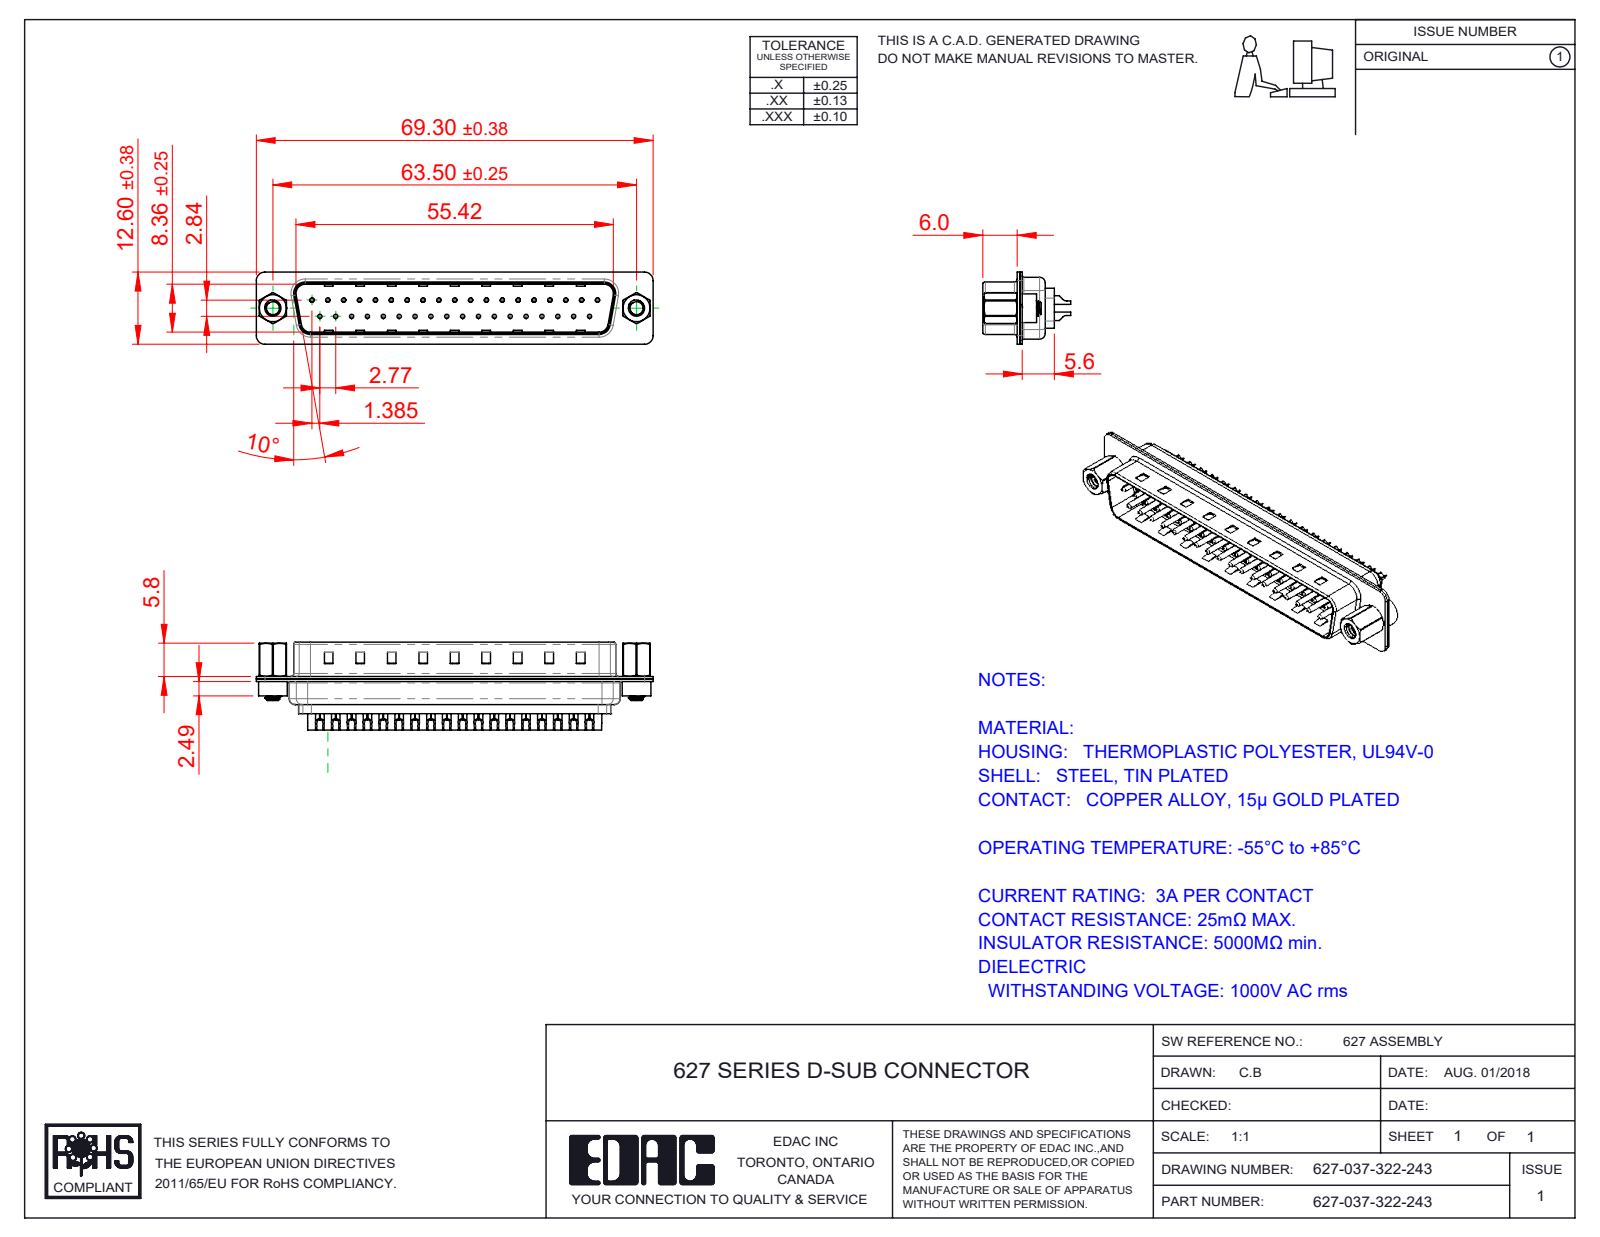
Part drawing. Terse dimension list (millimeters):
name: 627 Contact Row 2_22L; 627 Contact Row 1_22L; 627 4-40 Threaded Rivet; 627 4-40 Hex Standoff (+4 more)
written by: SolidWorks 2020 (CONFIG_CONTROL_DESIGN)
unit: mm
bodies: 44 solids, 2902 faces (743 planar, 1284 cylindrical, 875 other)
size: 69.3 × 15.35 × 12.6
volume: 3 922 mm³; area: 11 229 mm²
holes: 37× ⌀0.35, 37× ⌀1.1, 37× ⌀1.6, 2× ⌀2.26, 2× ⌀2.29, 2× ⌀4, 2× ⌀4.8
bosses: 37× ⌀2, 37× ⌀1.5, 37× ⌀0.75, 2× ⌀5, 2× ⌀4.9, 2× ⌀2.79
rounds: 16× R1.5, 12× R2, 8× R0.5, 8× R1.6, 6× R1, 4× R0.25, 4× R0.6, 4× R0.65
face distances: 0.4, 0.82, 9.58, 0.45, 8.76, 1.5, 0.9, 1.4, 6.05, 6.5
hole spacings: 3.16, 2.77, 5.54, 8.31, 5.04, 10.1, 11.08, 12.78
